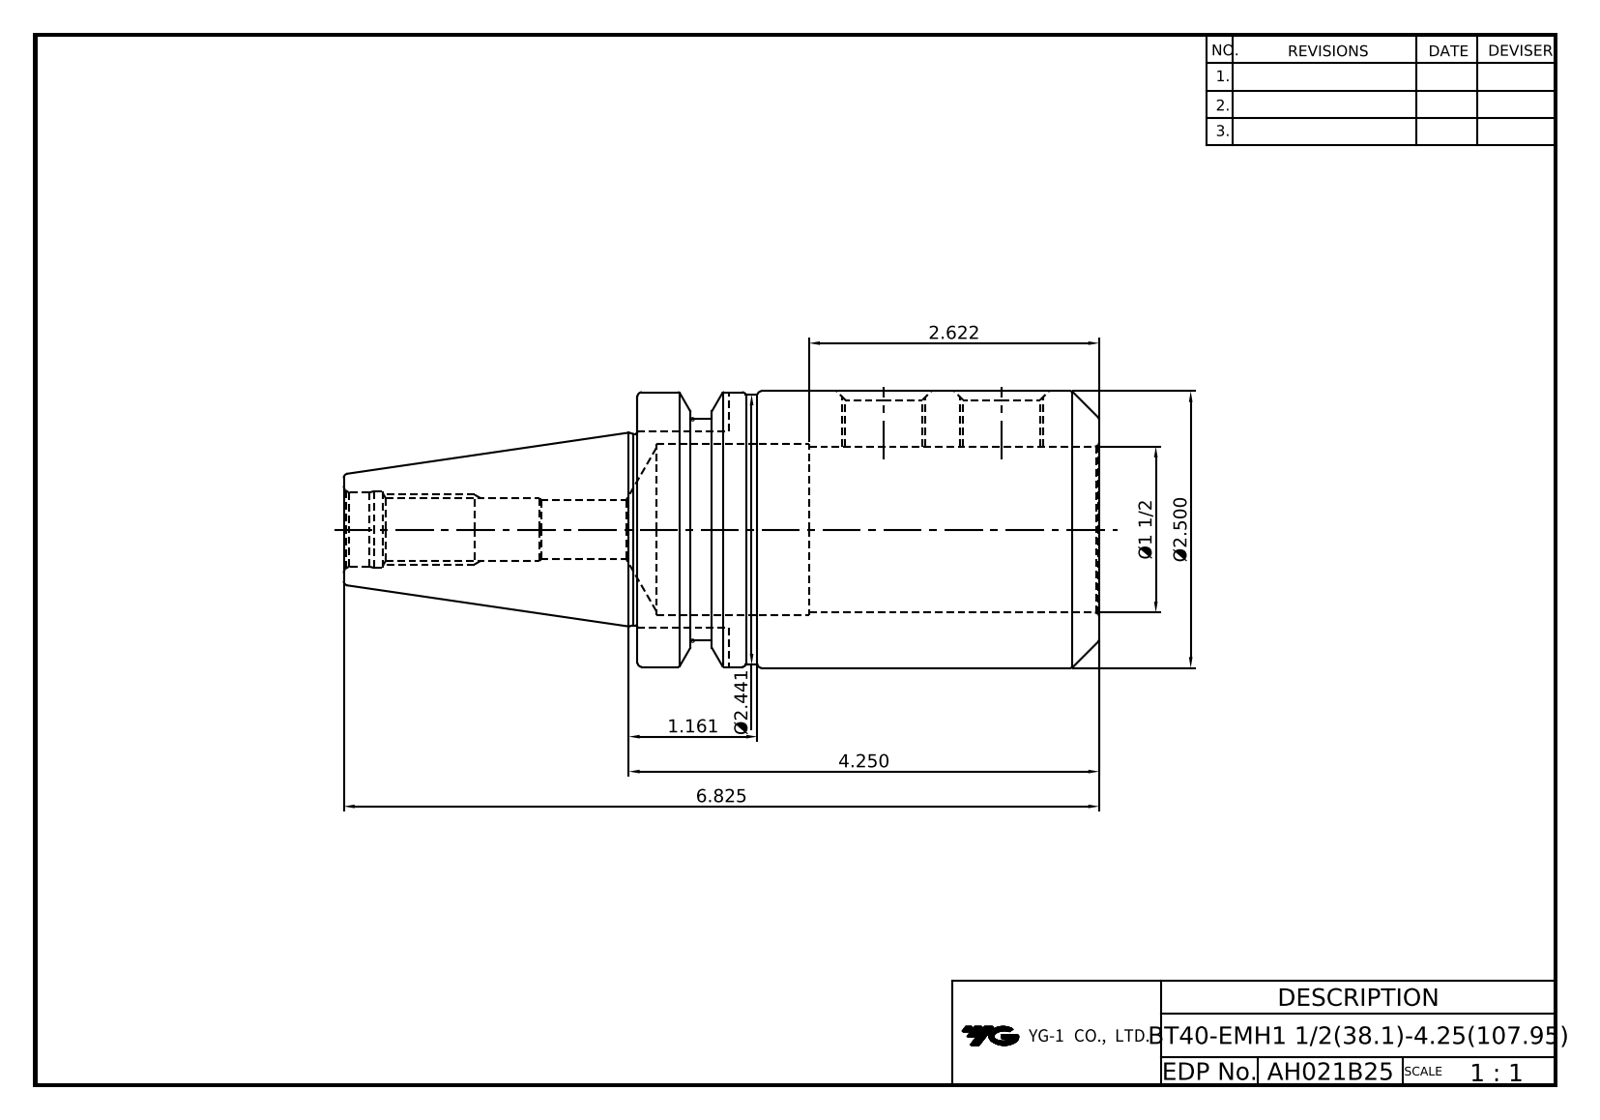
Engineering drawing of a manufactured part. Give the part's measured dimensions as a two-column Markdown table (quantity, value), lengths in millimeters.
| quantity | value |
| --- | --- |
| part name | LO-BT40-EMH38.1-107.95 |
| STEP written by | Autodesk Inventor 2022 (AUTOMOTIVE_DESIGN) |
| units | millimeters |
| bodies | 1 solid, 58 faces (16 planar, 18 cylindrical, 24 other) |
| overall size | 173.35 × 63.5 × 63.5 |
| volume | 247 509 mm³ |
| surface area | 49 681 mm² |
| round holes (diameter × count) | 17.32 × 2, 13.5 × 1, 13.84 × 1, 17 × 1, 17.6 × 1, 38.1 × 1, 39.3 × 1 |
| round bosses / shafts (diameter × count) | 63.5 × 1, 63 × 1, 62 × 1, 52.6 × 1, 44 × 1 |
| partial cylindrical surfaces (radius × count) | 8.05 × 1 |
| main face-to-face distances | 105.95, 45.2, 16.1, 67.4, 173.35, 84.5, 17.1, 88.85, 71.75, 4.35 |
| hole center spacings | 27 |
